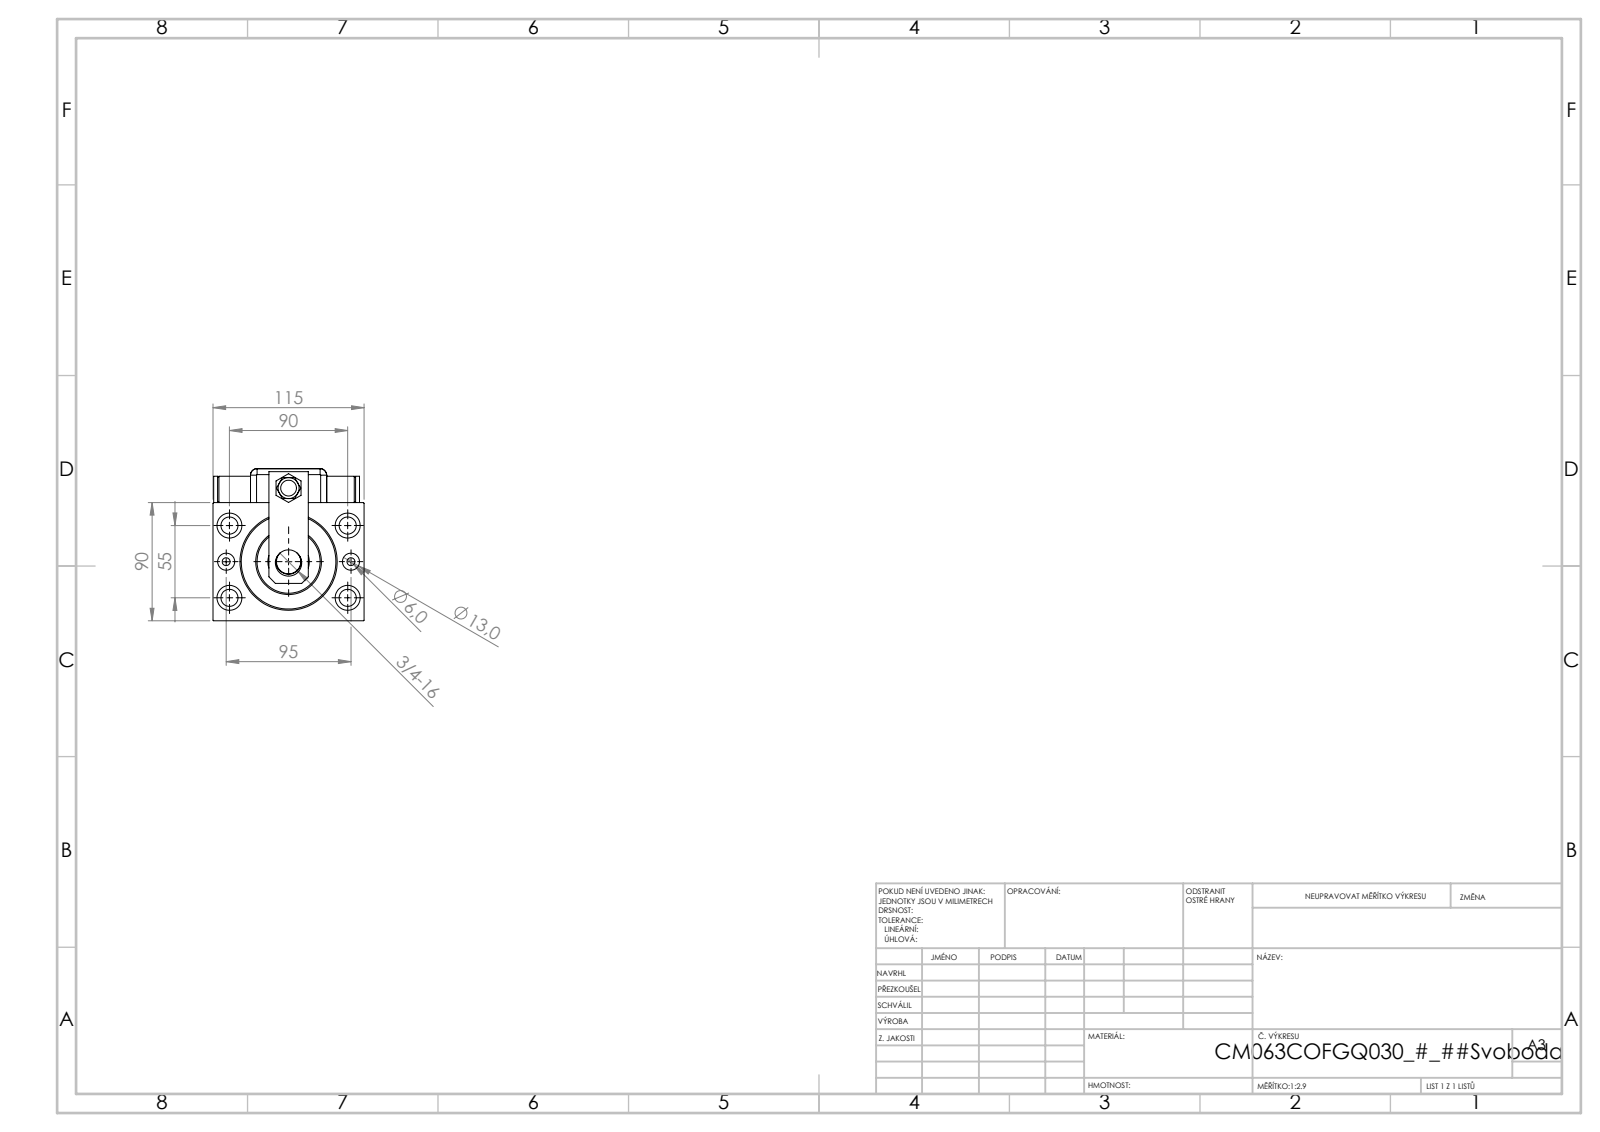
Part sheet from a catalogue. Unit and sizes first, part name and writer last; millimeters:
Units: millimetres
Overall size (bounding box): 160.46 × 115.8 × 115
Round holes (diameter × count): ⌀13 ×7, ⌀19 ×4, ⌀4 ×2, ⌀6 ×2, ⌀8 ×2, ⌀12 ×1, ⌀14 ×1, ⌀18.5 ×1, ⌀20 ×1, ⌀28 ×1, ⌀31.5 ×1, ⌀63 ×1
Round bosses / shafts (diameter × count): ⌀20 ×3, ⌀16 ×2, ⌀14 ×2, ⌀6 ×2, ⌀50 ×1
Partial cylindrical surfaces — rounded edges, fillets, slot ends (radius × count): R5 ×9, R10 ×1, R13.5 ×1
Main face-to-face distances: 90, 3, 115, 108, 90.5, 17.5, 13.5, 8, 25.8, 115.8
Hole centre spacings: 27.61, 52.74, 53.27, 96.5, 47.5, 47.51, 52.22, 55
Volume: 1 115 000 mm³ · Surface area: 196 345 mm²
Bodies: 13 solids, 1245 faces (615 planar, 113 cylindrical, 517 other)
Part name (STEP PRODUCT): NUT_D13; NUT_D19; MAGNETIC SWITCH Q; KRYT (+7 more)
STEP written by: SolidWorks 2019 (CONFIG_CONTROL_DESIGN)
